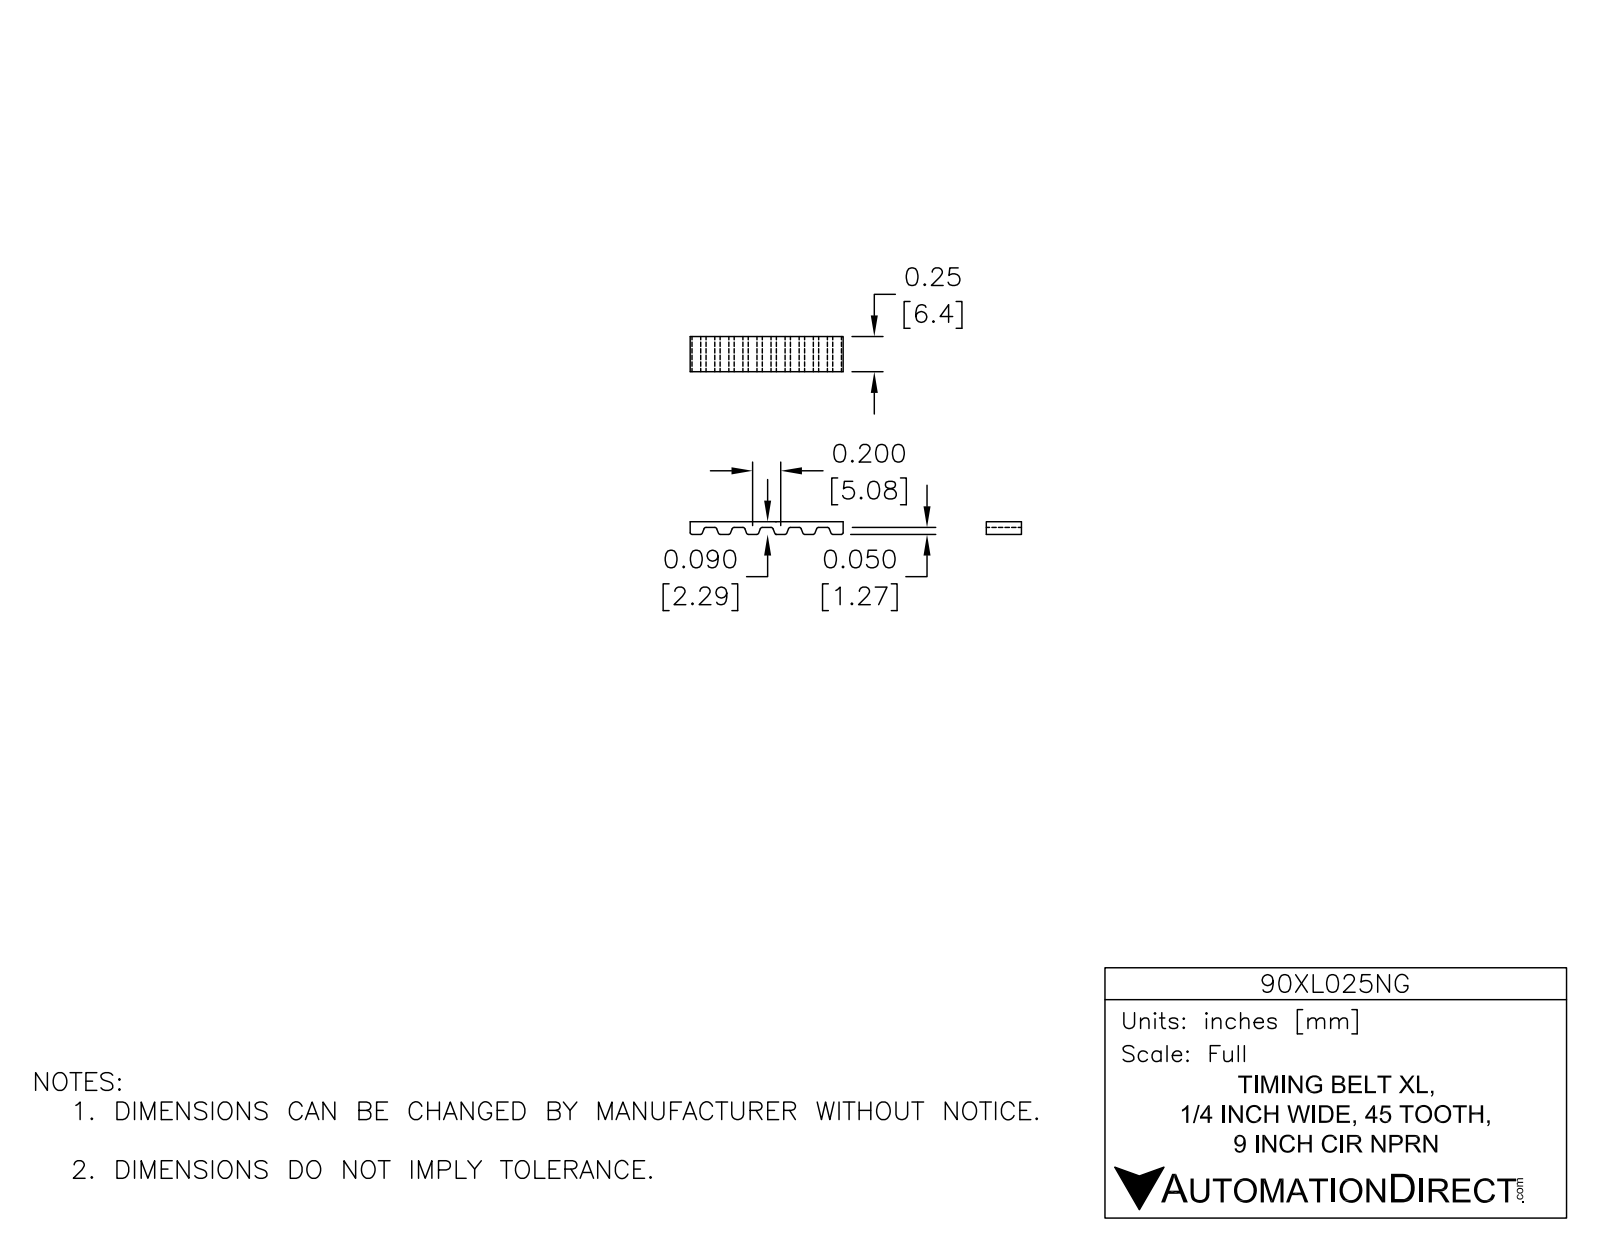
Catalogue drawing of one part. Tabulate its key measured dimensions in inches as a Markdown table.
| quantity | value |
| --- | --- |
| part name | 90XL025NG |
| STEP written by | SolidWorks 2014 (AUTOMOTIVE_DESIGN) |
| units | inches |
| bodies | 1 solid, 388 faces (154 planar, 234 cylindrical, 0 other) |
| overall size | 3.358 × 2 × 0.25 |
| volume | 0.121 in³ |
| surface area | 6.029 in² |
| partial cylindrical surfaces (radius × count) | 0.015 × 180, 0.96 × 2, 1 × 2 |
| main face-to-face distances | 0.25, 2, 0.04, 1.96, 1.92, 0.352, 0.176, 0.528, 0.176, 0.881 |
